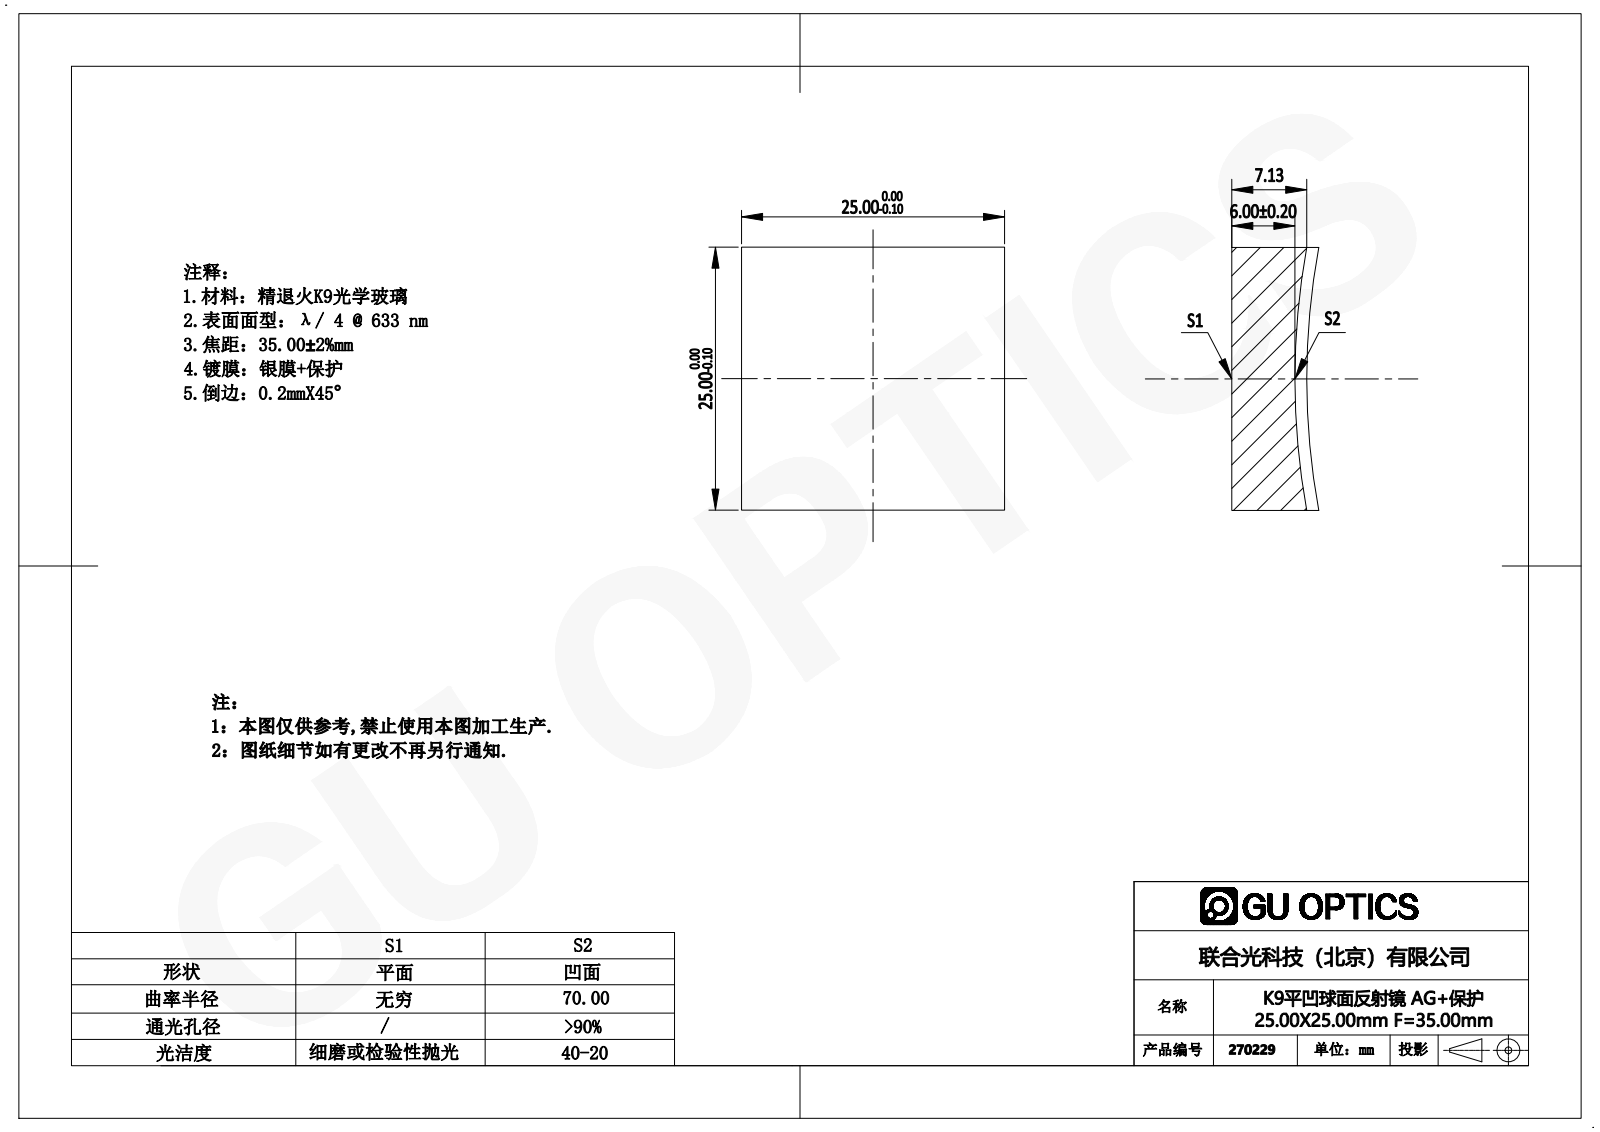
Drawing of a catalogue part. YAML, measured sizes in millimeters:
part_name: "270034"
step_written_by: "SolidWorks 2019 (AUTOMOTIVE_DESIGN)"
units: millimeters
bodies: {solids: 1, faces: 7, planar: 5, cylindrical: 0, other: 2}
overall_size: [25, 25, 8.27]
volume: 4219
surface_area: 2007
face_to_face_distances: [25]
